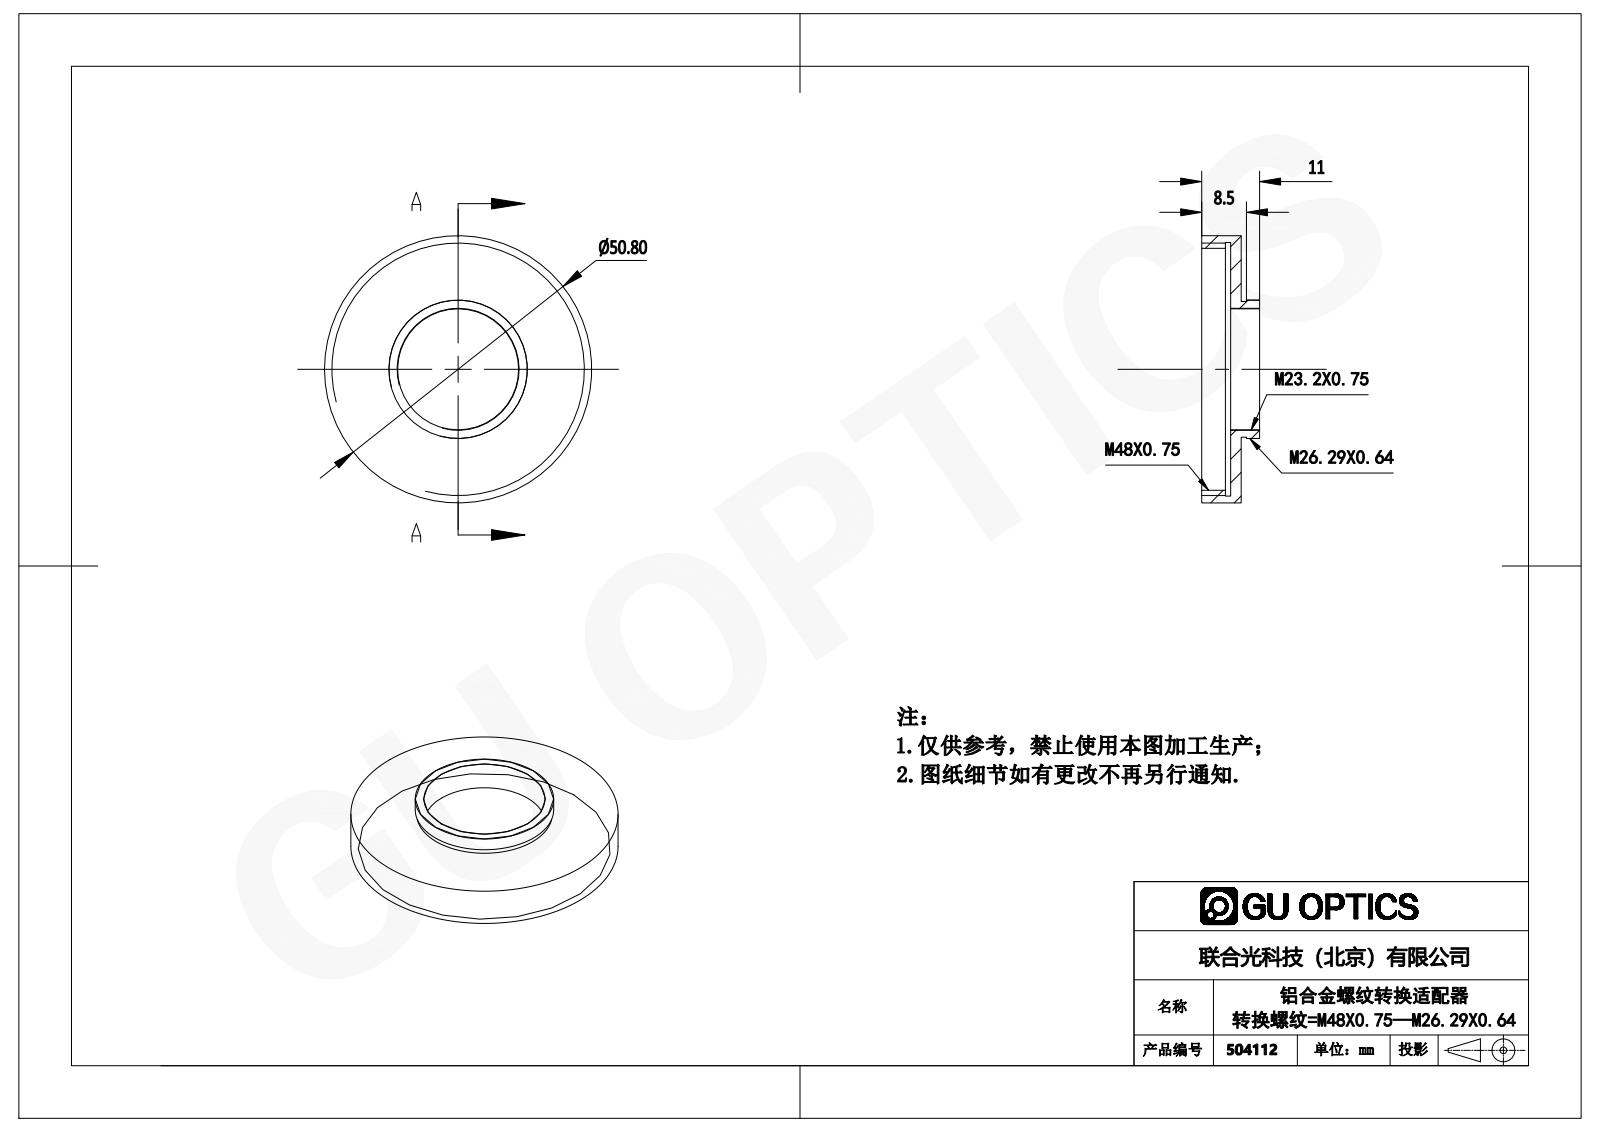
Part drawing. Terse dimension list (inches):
name: 504112
written by: SolidWorks 2016 (AUTOMOTIVE_DESIGN)
unit: in
bodies: 1 solid, 18 faces (6 planar, 12 cylindrical, 0 other)
size: 2 × 2 × 0.433
volume: 0.335 in³; area: 9.726 in²
holes: 1× ⌀0.906, 1× ⌀1.811, 1× ⌀1.898
bosses: 1× ⌀2, 1× ⌀1.036, 1× ⌀1.016
face distances: 0.079, 0.217, 0.295, 0.039, 0.118, 0.177, 0.433, 0.256, 0.138, 0.335
